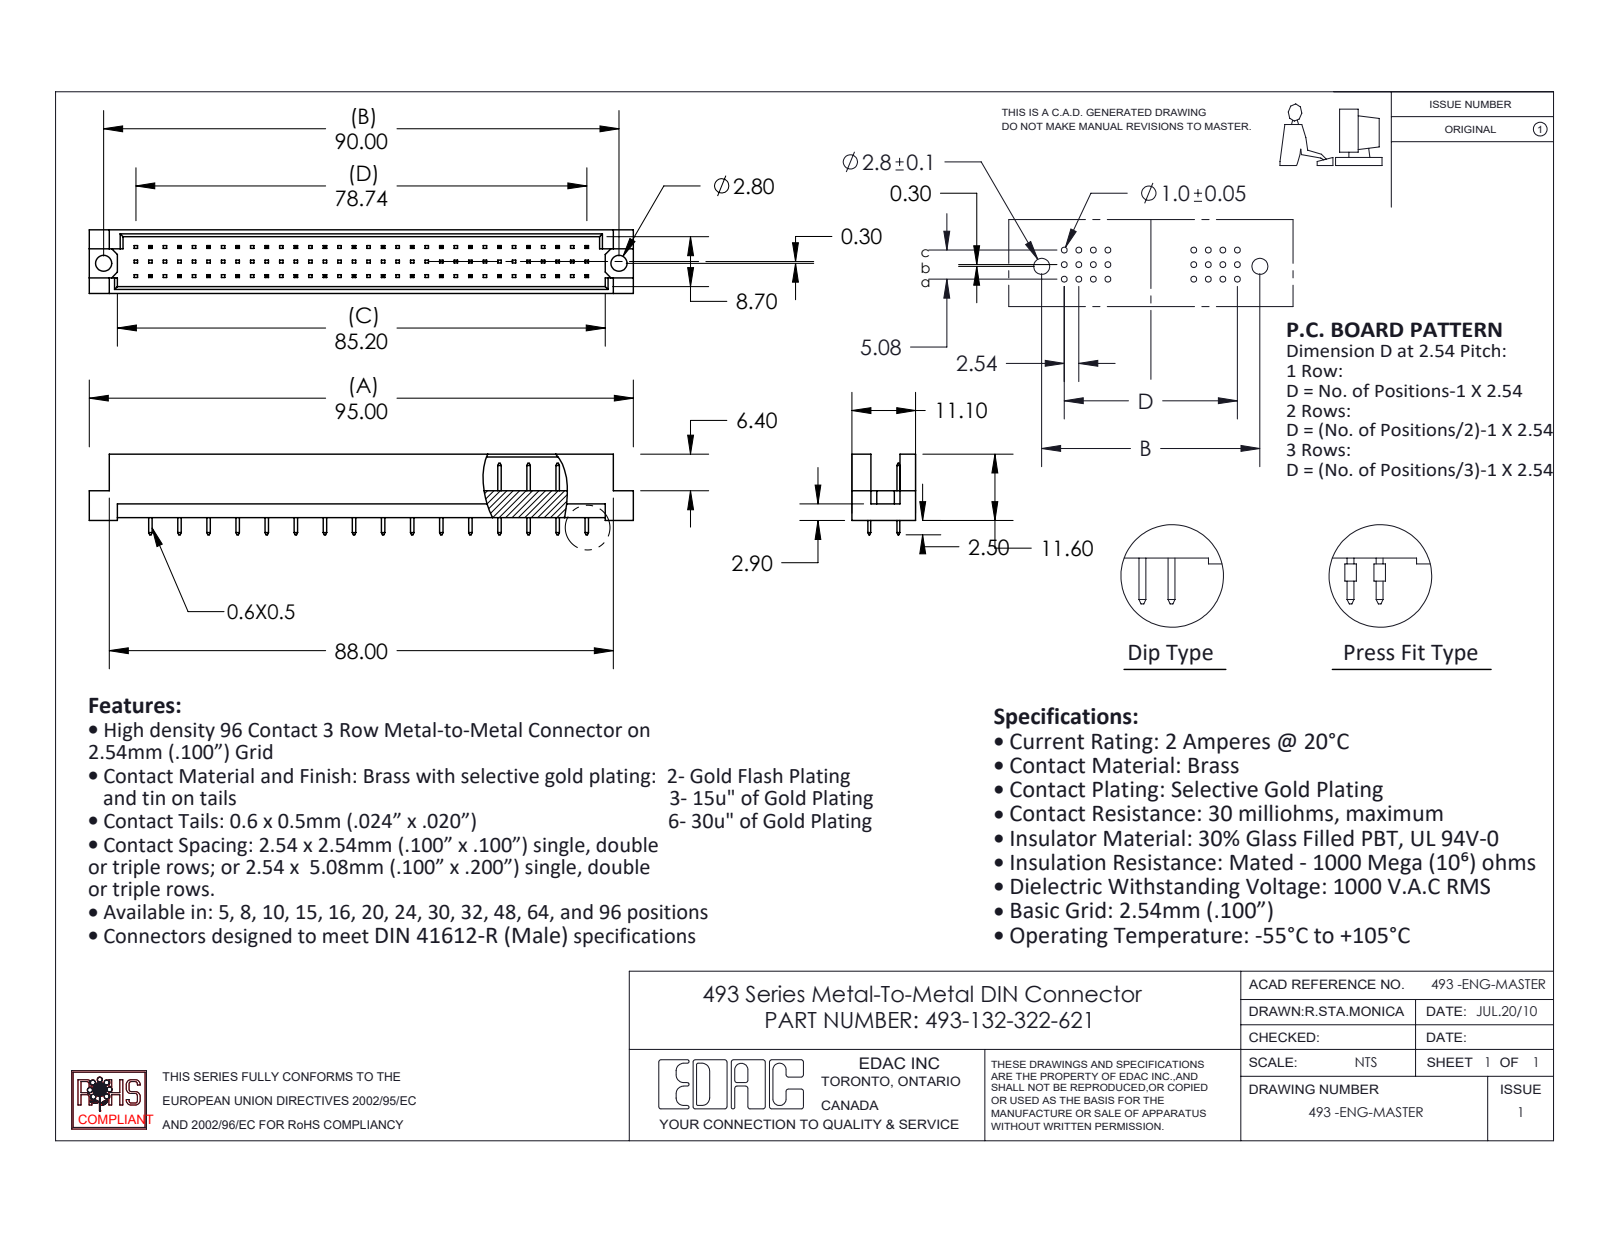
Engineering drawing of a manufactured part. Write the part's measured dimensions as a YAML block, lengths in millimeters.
part_name: "493 Part_96; 493-132-322-621; 493-290_22"
step_written_by: "SolidWorks 2020 (CONFIG_CONTROL_DESIGN)"
units: millimeters
bodies: {solids: 33, faces: 884, planar: 880, cylindrical: 4, other: 0}
overall_size: [95, 14.1, 11.1]
volume: 5776
surface_area: 7342
round_holes:
  - {diameter: 2.8, count: 2}
face_to_face_distances: [1.2, 9.9, 11.1, 8.7, 4.7, 5.08, 0.5, 2.76, 3.26, 7.84]
hole_center_spacings: [90]
